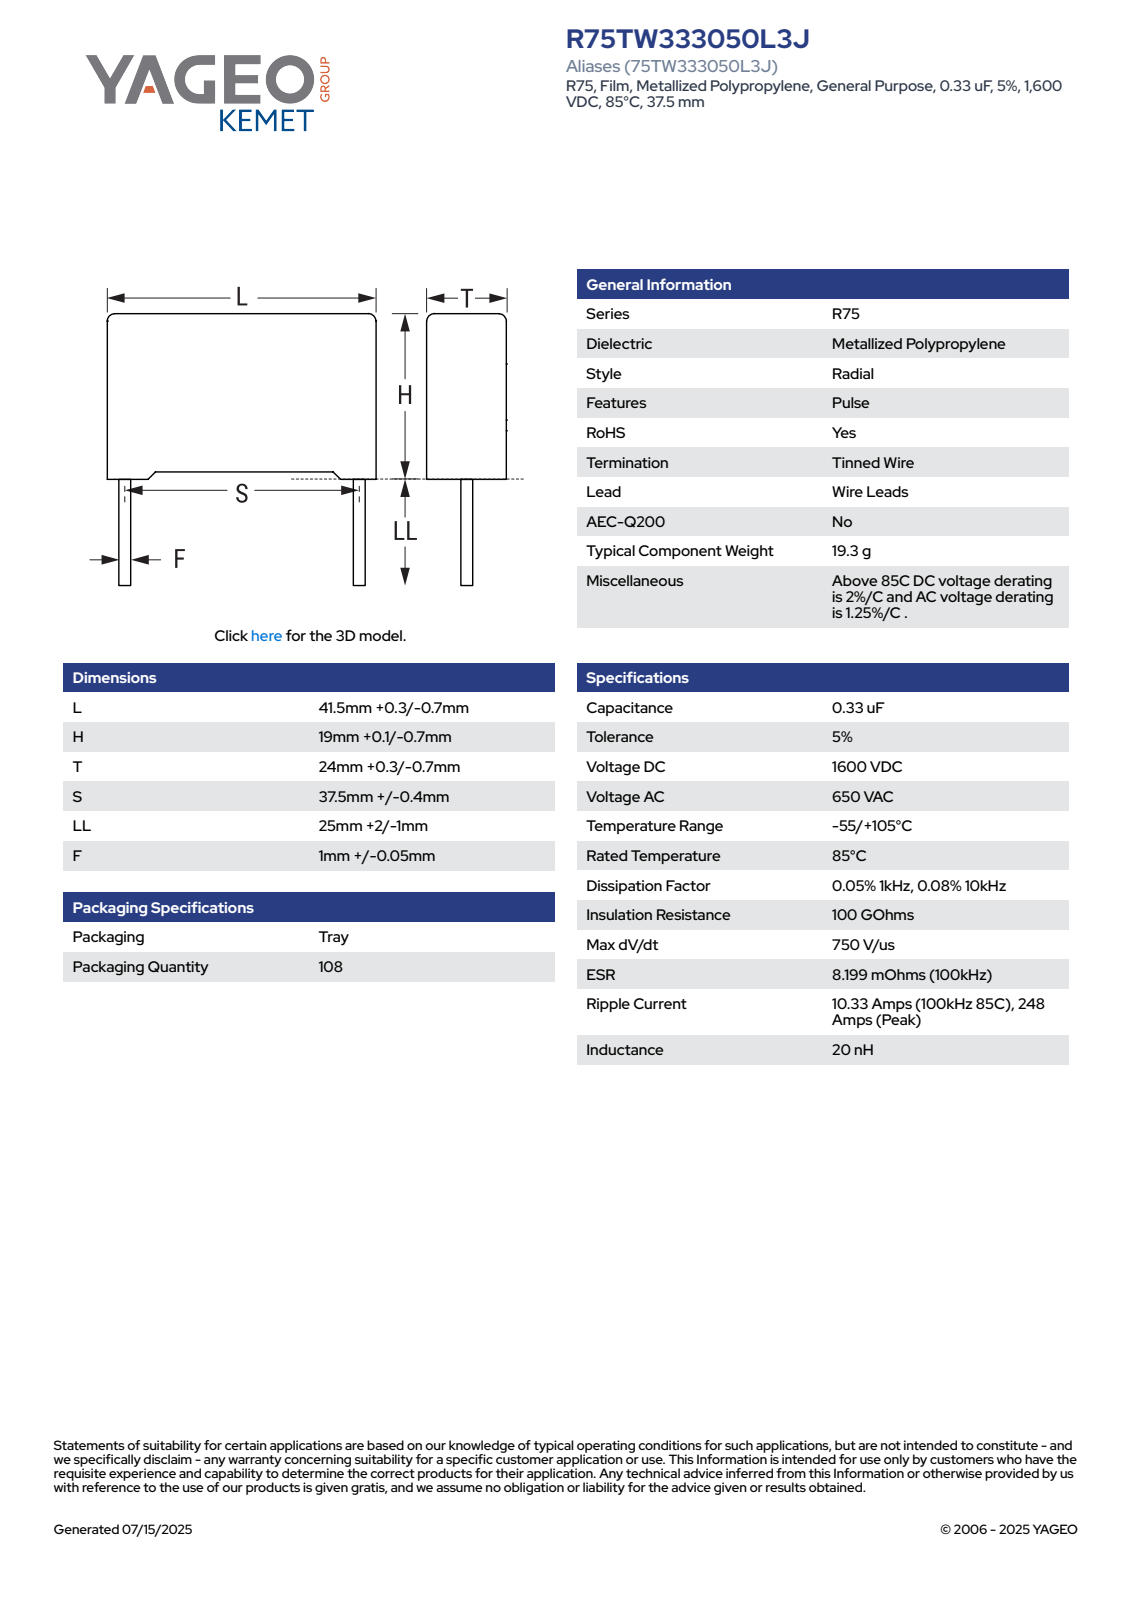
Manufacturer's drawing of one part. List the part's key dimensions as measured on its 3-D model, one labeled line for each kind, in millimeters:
Part name (STEP PRODUCT): CFR_RB2_41.5X19X24_L41.8H19.1T24.3S37.5LL27F1.05
STEP written by: SolidWorks 2021 (AUTOMOTIVE_DESIGN)
Units: millimetres
Bodies: 4 solids, 85 faces (77 planar, 8 cylindrical, 0 other)
Overall size (bounding box): 46.1 × 41.8 × 24.3
Volume: 18 751 mm³ · Surface area: 4 846 mm²
Round bosses / shafts (diameter × count): ⌀1.05 ×2
Partial cylindrical surfaces — rounded edges, fillets, slot ends (radius × count): R0.5 ×4
Main face-to-face distances: 18.35, 24.3, 41.8, 18.44, 0.66, 0.75, 19.1, 1.39, 40.41, 24.31
